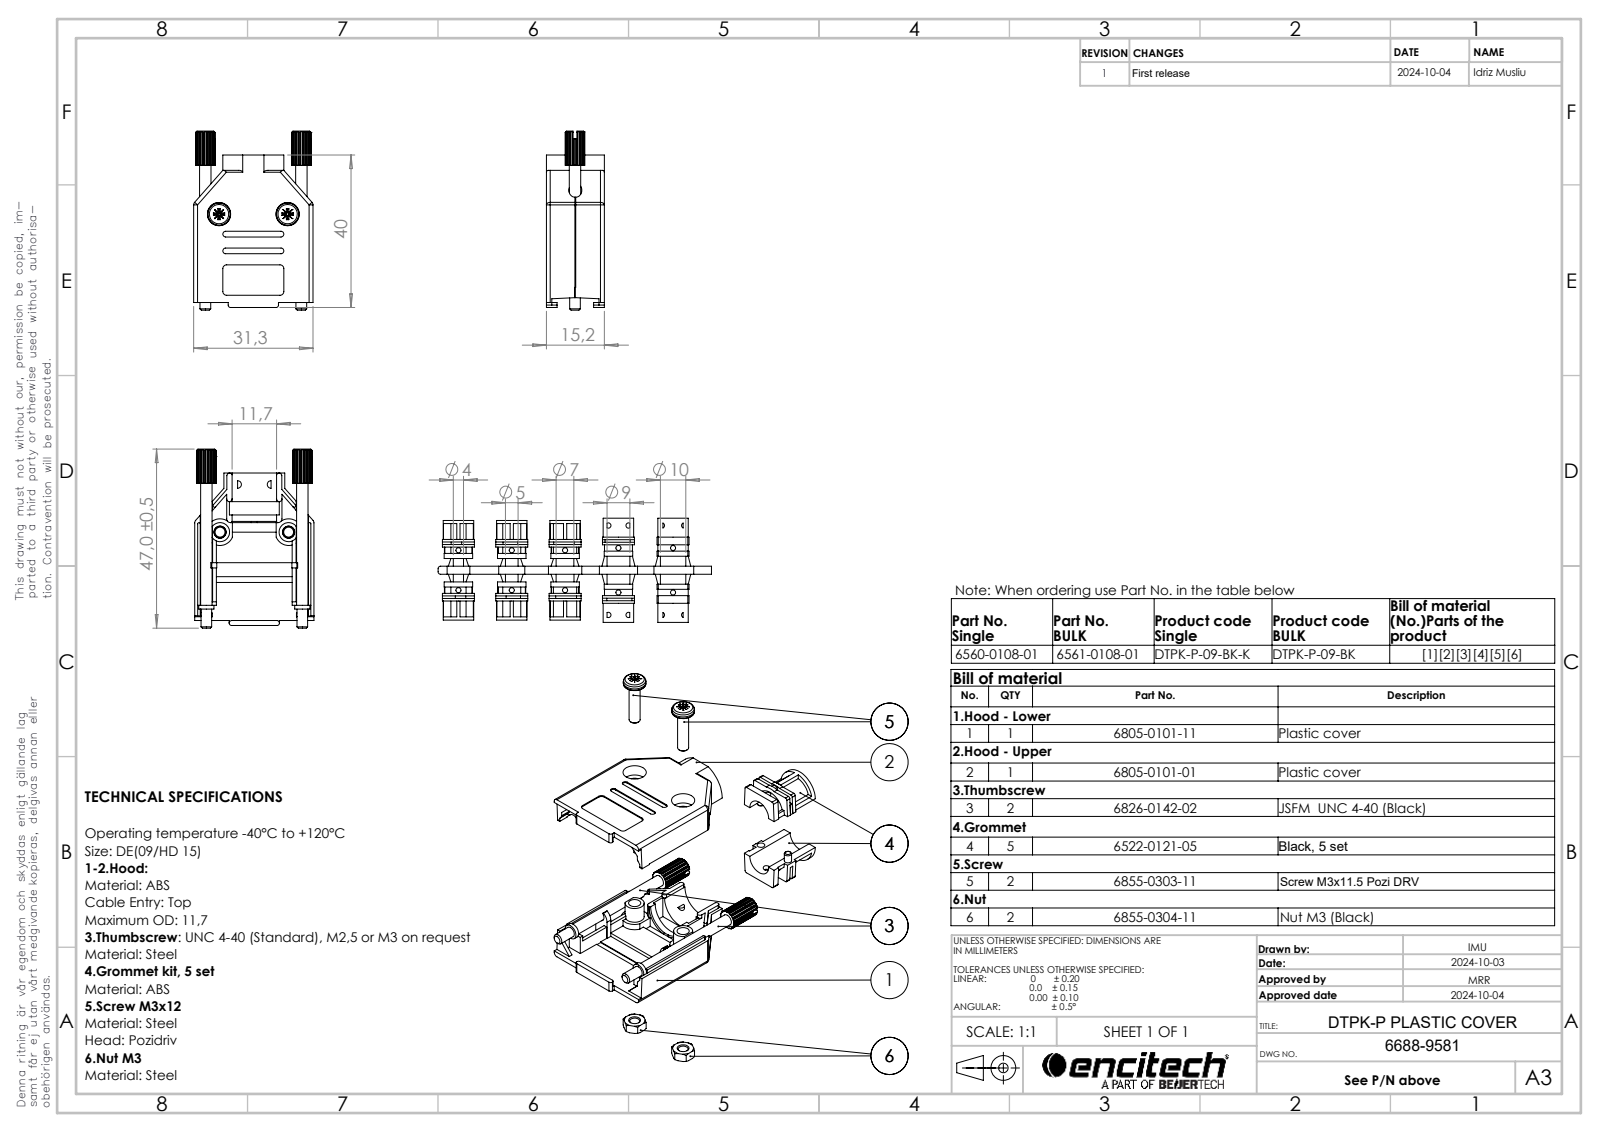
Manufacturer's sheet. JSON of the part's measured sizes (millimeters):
{"part_name": "6805-0101-11; 6688-9581; 6805-0101-01; 6855-0303-11 (+3 more)", "step_written_by": "SolidWorks 2021 (AUTOMOTIVE_DESIGN)", "units": "millimeters", "bodies": {"solids": 10, "faces": 868, "planar": 526, "cylindrical": 242, "other": 100}, "overall_size": [47, 31.3, 15.2], "volume_mm3": 7777, "surface_area_mm2": 12227, "round_holes": [[2, 3], [2.6, 2], [3.2, 2], [6.1, 2], [7, 1]], "round_bosses_or_shafts": [[5, 2], [4, 2], [3, 2], [2.9, 2], [2.8, 2], [1.9, 2], [11.6, 1], [9.2, 1]], "partial_cylinders_radius": [[1, 18], [0.5, 10], [0.1, 8], [0.75, 8], [0.7, 4], [1.6, 4], [5.91, 4], [0.15, 2]], "face_to_face_distances": [13.8, 1.4, 15.2, 1.6, 1, 1.1, 12.4, 29.7, 2.7, 14.9], "hole_center_spacings": [5.71, 7.34, 9.62, 15.29, 10, 18]}
